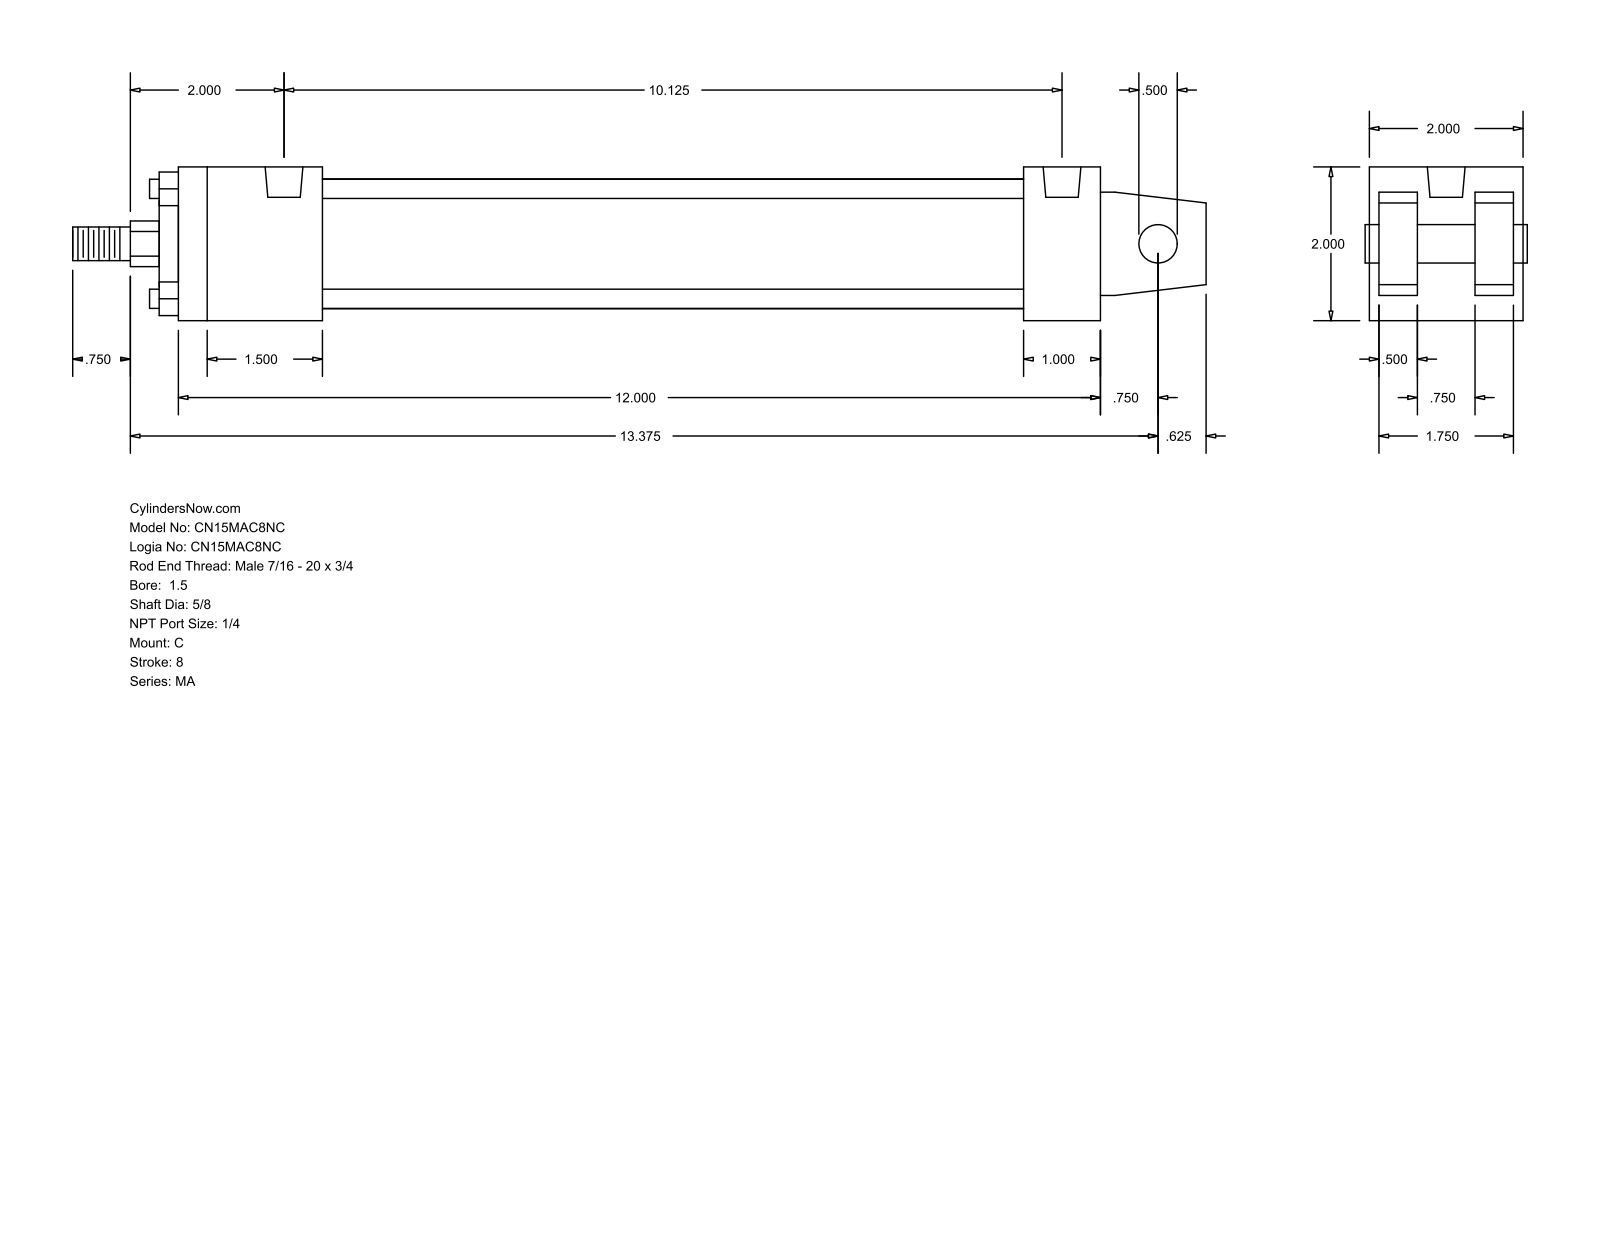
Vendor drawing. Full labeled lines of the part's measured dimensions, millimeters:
Part name (STEP PRODUCT): MA_C__0150_0.625
STEP written by: GSSL Pune (CONFIG_CONTROL_DESIGN)
Units: millimetres
Bodies: 0 solids, 103 faces (76 planar, 27 cylindrical, 0 other)
Overall size (bounding box): 374.65 × 50.8 × 50.8
Round holes (diameter × count): ⌀7.94 ×4, ⌀12.49 ×2
Round bosses / shafts (diameter × count): ⌀6.35 ×4, ⌀42.93 ×1, ⌀28.57 ×1, ⌀15.88 ×1, ⌀12.7 ×1, ⌀11.11 ×1
Partial cylindrical surfaces — rounded edges, fillets, slot ends (radius × count): R7.54 ×1
Main face-to-face distances: 50.8, 12.7, 34.93, 15.87, 3.17, 47.63, 31.76, 304.8, 279.39, 25.41
Hole centre spacings: 257.18
